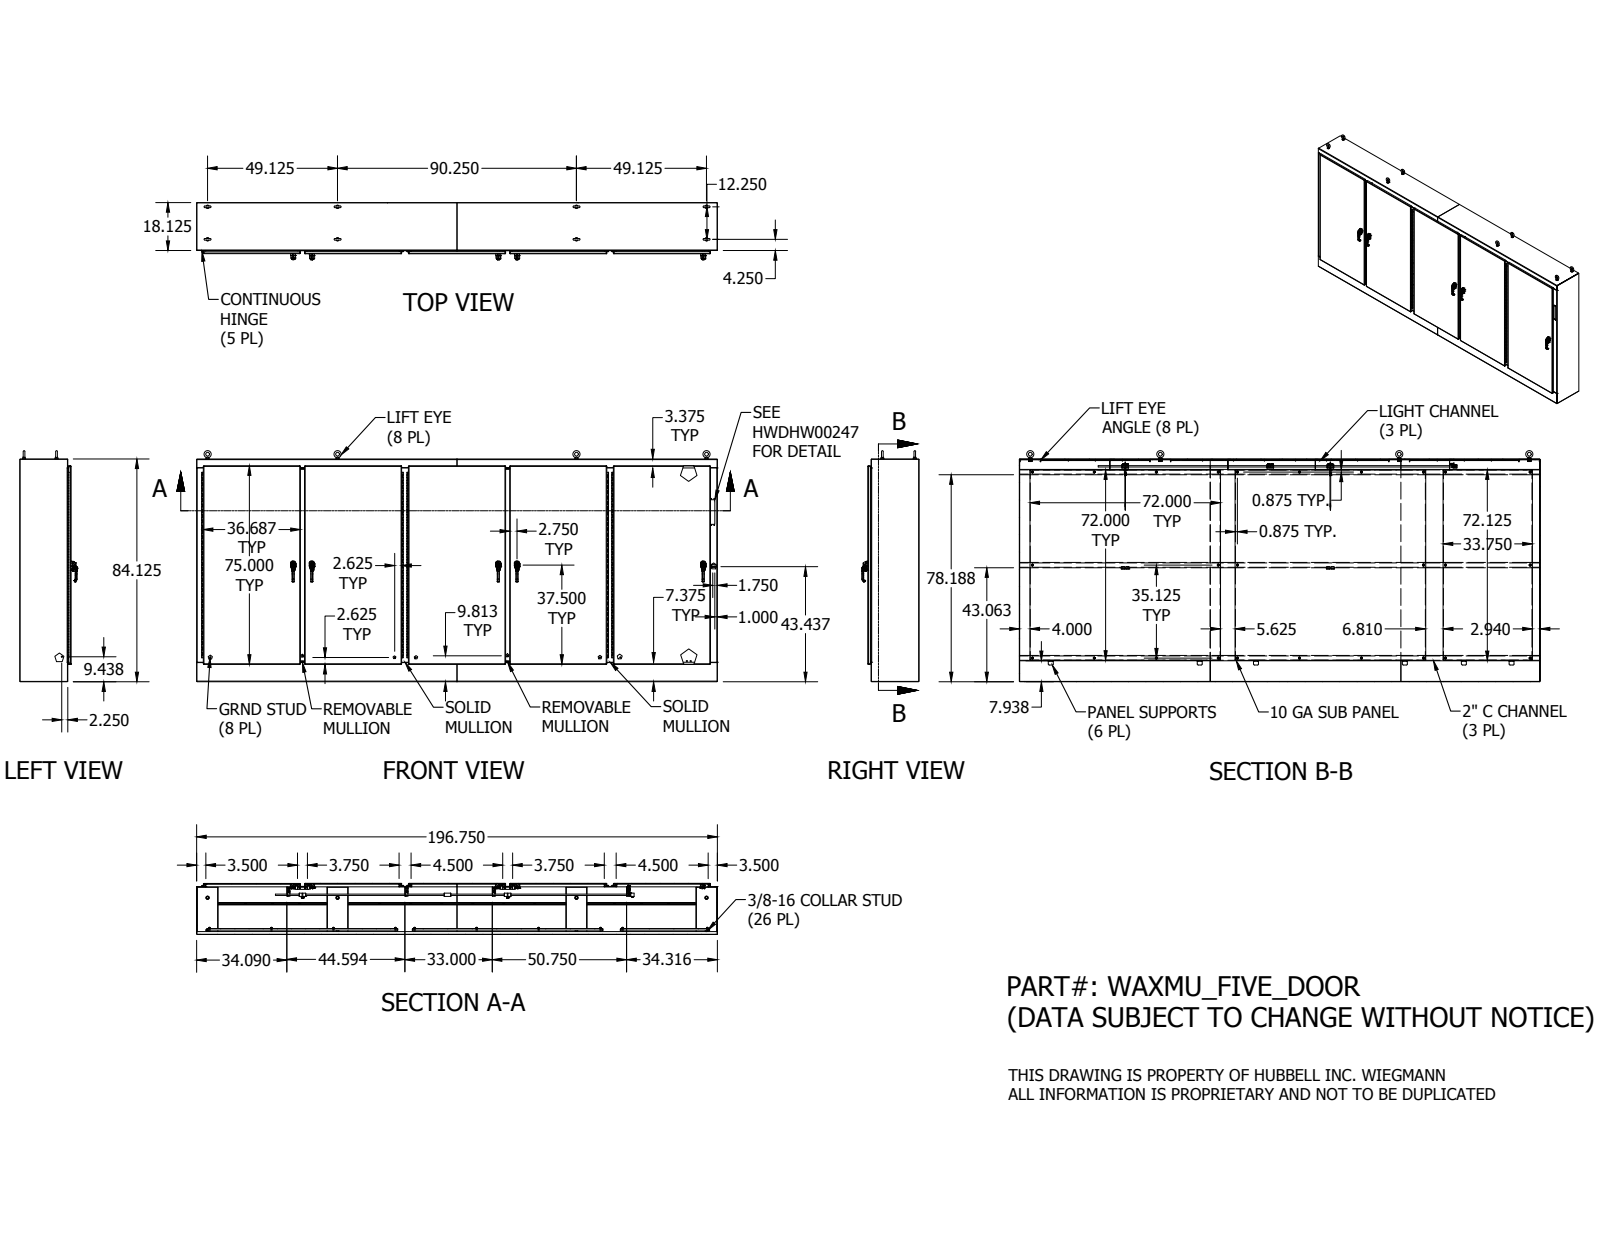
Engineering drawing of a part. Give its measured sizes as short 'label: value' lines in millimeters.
name: WAXMU_FIVE_DOOR_BACK_LARGE; WAXMU_FIVE_DOOR_BACK_SMALL; HFW1404-WAM5EWU; 3889 (+8 more)
written by: Autodesk Inventor 2014 (AUTOMOTIVE_DESIGN)
unit: mm
bodies: 550 solids, 21567 faces (9959 planar, 6965 cylindrical, 4643 other)
size: 4997.45 × 2216.09 × 548.73
volume: 136 400 000 mm³; area: 85 830 000 mm²
holes: 42× ⌀9.52, 40× ⌀6.35, 26× ⌀7.8, 26× ⌀14.29, 20× ⌀5.08, 20× ⌀7.02, 18× ⌀4.83, 18× ⌀7.33, 18× ⌀7.94, 18× ⌀8.51, 18× ⌀9.65, 15× ⌀5.4
bosses: 49× ⌀8.38, 44× ⌀6.35, 33× ⌀15.88, 29× ⌀9.52, 26× ⌀8.56, 19× ⌀12.7, 18× ⌀7.11, 17× ⌀14.29
rounds: 850× R0.5, 515× R0.3, 432× R0.51, 105× R0.47, 90× R1.27, 78× R1.59, 67× R2, 55× R1
face distances: 3.18, 3.17, 434.46, 488.43, 53.98, 53.97, 50.8, 57.15, 1.59, 431.28
hole spacings: 1968.5, 1784.35, 27.99, 1880.87, 3540.12, 1.97, 1247.78, 1285.99
